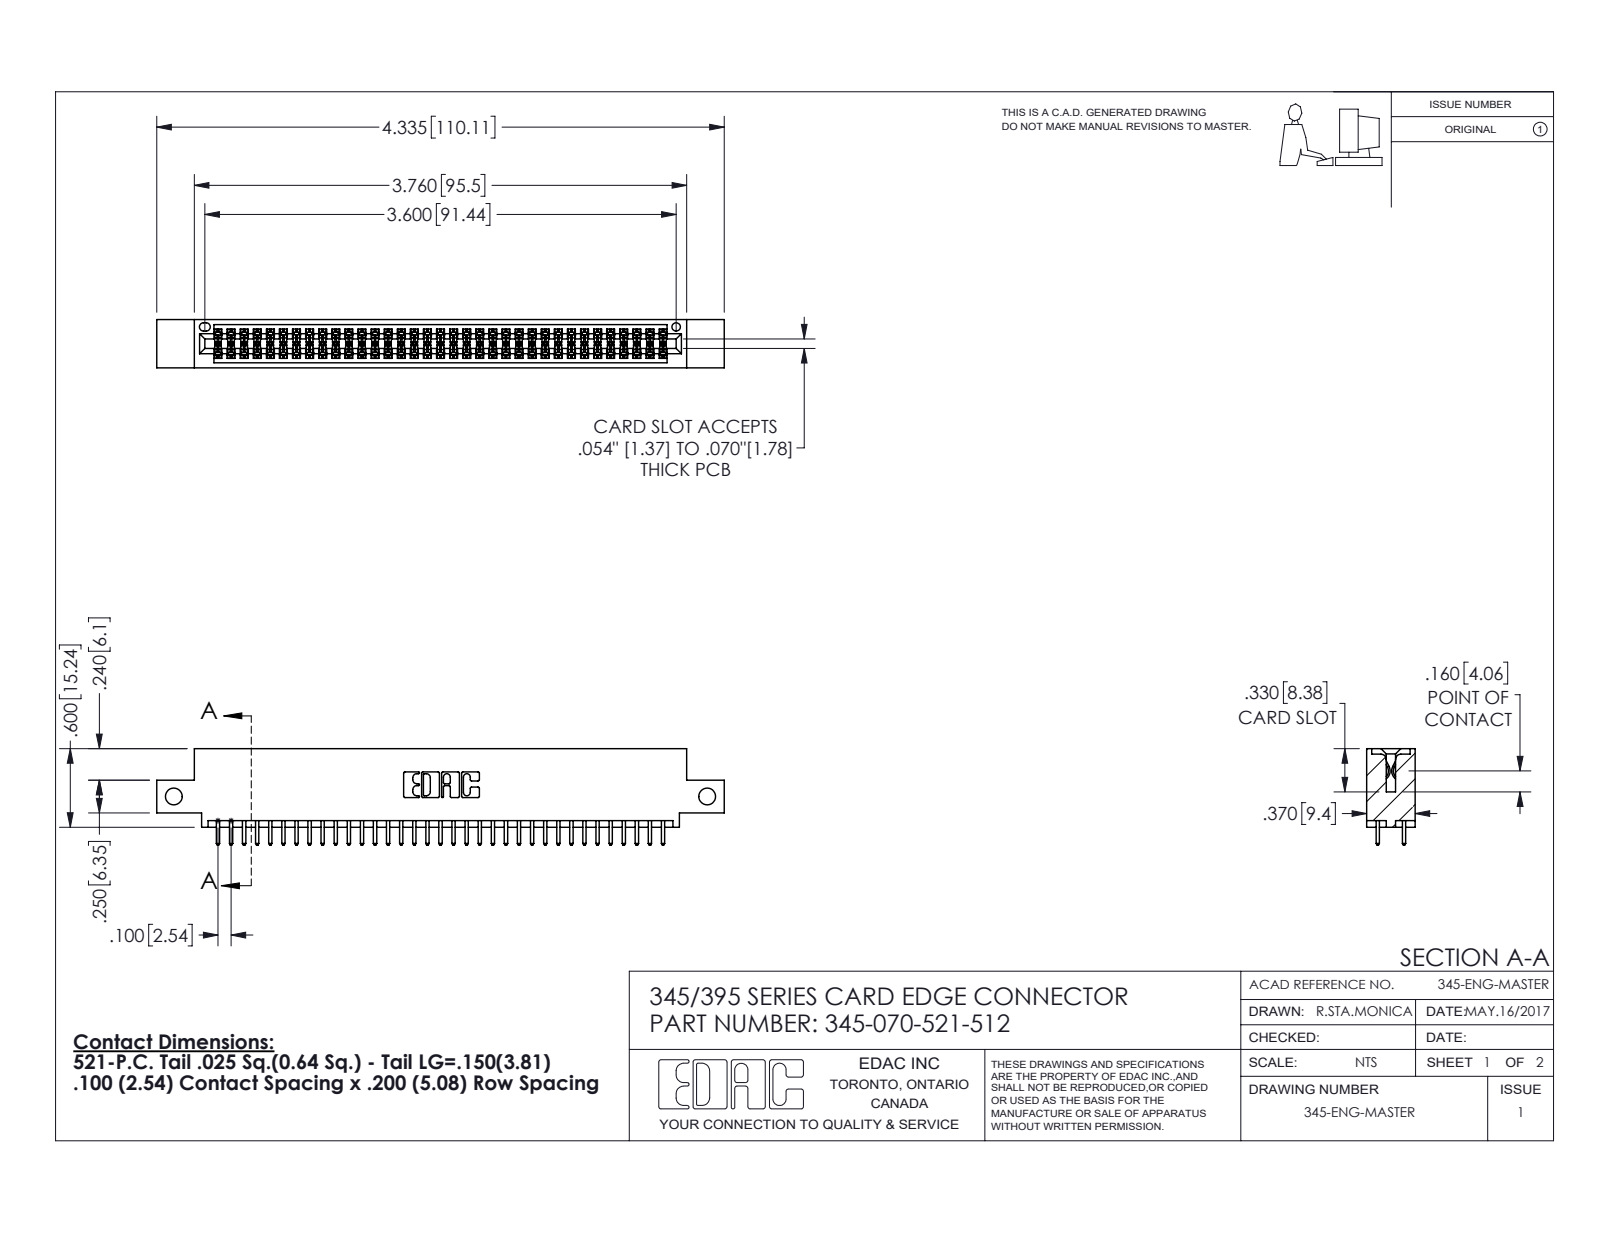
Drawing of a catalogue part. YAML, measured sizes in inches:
part_name: "345 Part_0.110 Offset - Side Mount; 345-292-001_345-293-121; 345-070-521-512"
step_written_by: "SolidWorks 2016 (CONFIG_CONTROL_DESIGN)"
units: inches
bodies: {solids: 71, faces: 3630, planar: 2394, cylindrical: 1236, other: 0}
overall_size: [4.335, 0.737, 0.37]
volume: 0.637
surface_area: 23.36
round_holes:
  - {diameter: 0.128, count: 2}
  - {diameter: 0.064, count: 1}
partial_cylinders:
  - {radius: 0.006, count: 105}
  - {radius: 0.01, count: 70}
  - {radius: 0.01, count: 22}
  - {radius: 0.007, count: 6}
  - {radius: 0.031, count: 6}
  - {radius: 0.026, count: 3}
  - {radius: 0.014, count: 2}
  - {radius: 0.019, count: 2}
face_to_face_distances: [0.298, 0.072, 0.2, 0.37, 0.098, 0.272, 0.025, 0.225, 0.175, 0.149]
hole_center_spacings: [4.075]
